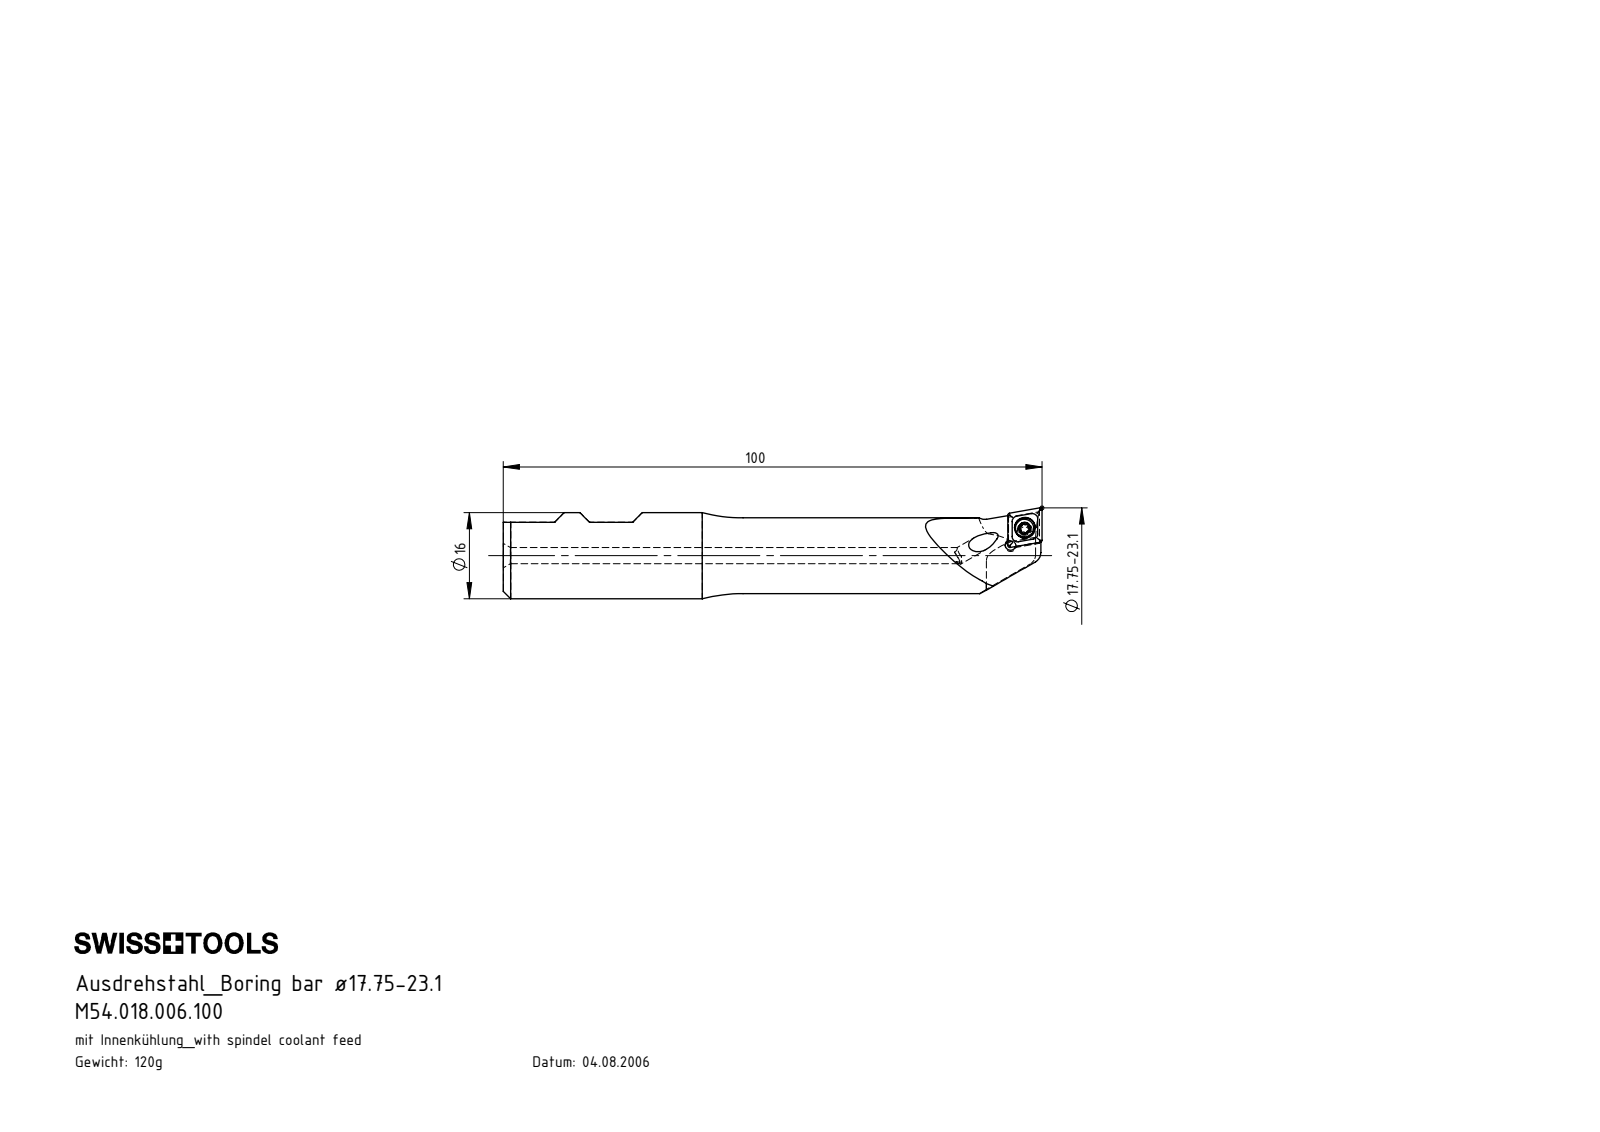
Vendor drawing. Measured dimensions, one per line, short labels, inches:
name: CCMT060204; B18-WCA.K11.100_A; WCA-ER2.001.006_A; B18.WCA.K11.100
written by: SolidWorks 2017 (AUTOMOTIVE_DESIGN)
unit: in
bodies: 3 solids, 101 faces (33 planar, 27 cylindrical, 41 other)
size: 3.937 × 0.665 × 0.63
volume: 0.932 in³; area: 9.038 in²
holes: 2× ⌀0.118, 1× ⌀0.079, 1× ⌀0.081, 1× ⌀0.11, 1× ⌀0.152
bosses: 1× ⌀0.63, 1× ⌀0.553, 1× ⌀0.134, 1× ⌀0.098
rounds: 6× R0.008, 5× R0.014, 1× R0.014, 1× R0.079, 1× R0.283, 1× R0.335, 1× R0.394
face distances: 0.086, 0.232, 0.318, 0.404, 0.326, 0.094, 3.691, 0.291, 0.058, 0.028
hole spacings: 0.159, 0.163
